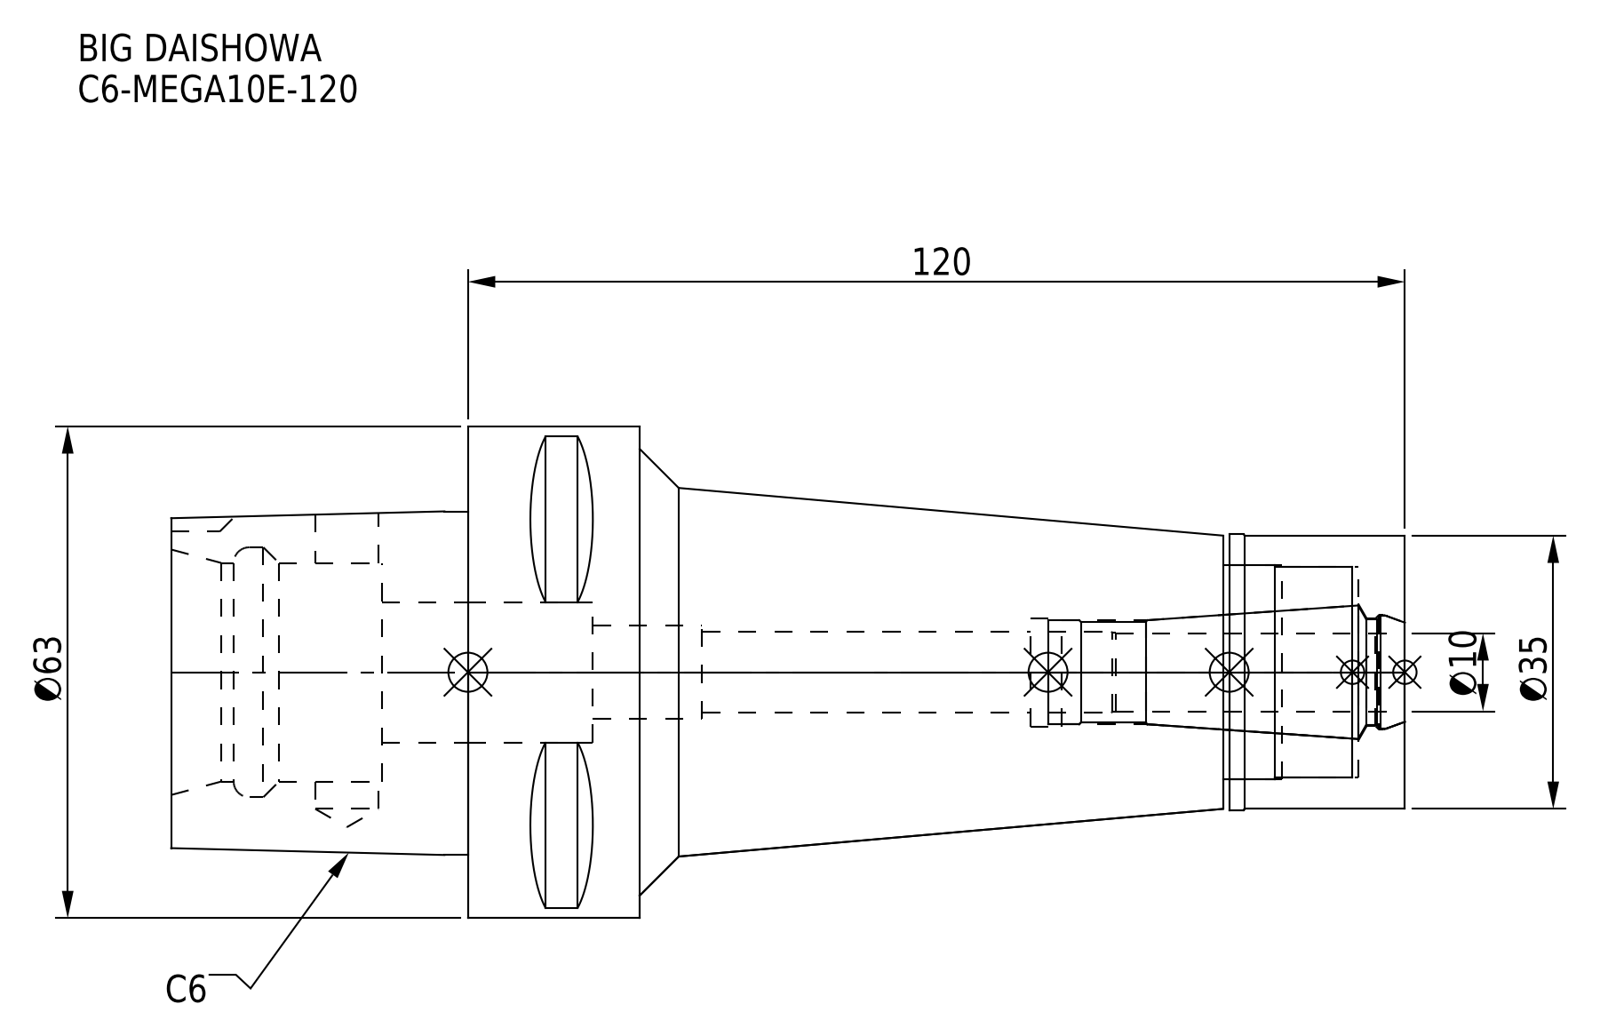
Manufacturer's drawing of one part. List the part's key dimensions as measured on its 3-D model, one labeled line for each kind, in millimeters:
Part name (STEP PRODUCT): C6-MEGA10E-120-100-FreeParts; DXF_TEMP_ASSY_ASM_4_ASM.stp; C6-MEGA10E-120_1.stp; C6-MEGA10E-120-100_ASM.stp (+3 more)
STEP written by: SolidWorks 2019 (CONFIG_CONTROL_DESIGN)
Units: millimetres
Bodies: 2 solids, 100 faces (37 planar, 39 cylindrical, 24 other)
Overall size (bounding box): 158 × 63 × 63
Volume: 209 173 mm³ · Surface area: 39 505 mm²
Round holes (diameter × count): ⌀8.1 ×1, ⌀10.4 ×1, ⌀12 ×1, ⌀13.3 ×1, ⌀13.8 ×1, ⌀13.9 ×1, ⌀14.7 ×1, ⌀18 ×1, ⌀27 ×1, ⌀27.5 ×1, ⌀28 ×1, ⌀32 ×1
Round bosses / shafts (diameter × count): ⌀63 ×1, ⌀35.3 ×1, ⌀35 ×1
Partial cylindrical surfaces — rounded edges, fillets, slot ends (radius × count): R5 ×1
Main face-to-face distances: 120, 98, 22, 38, 60, 27, 158, 6, 22.5, 75.5
